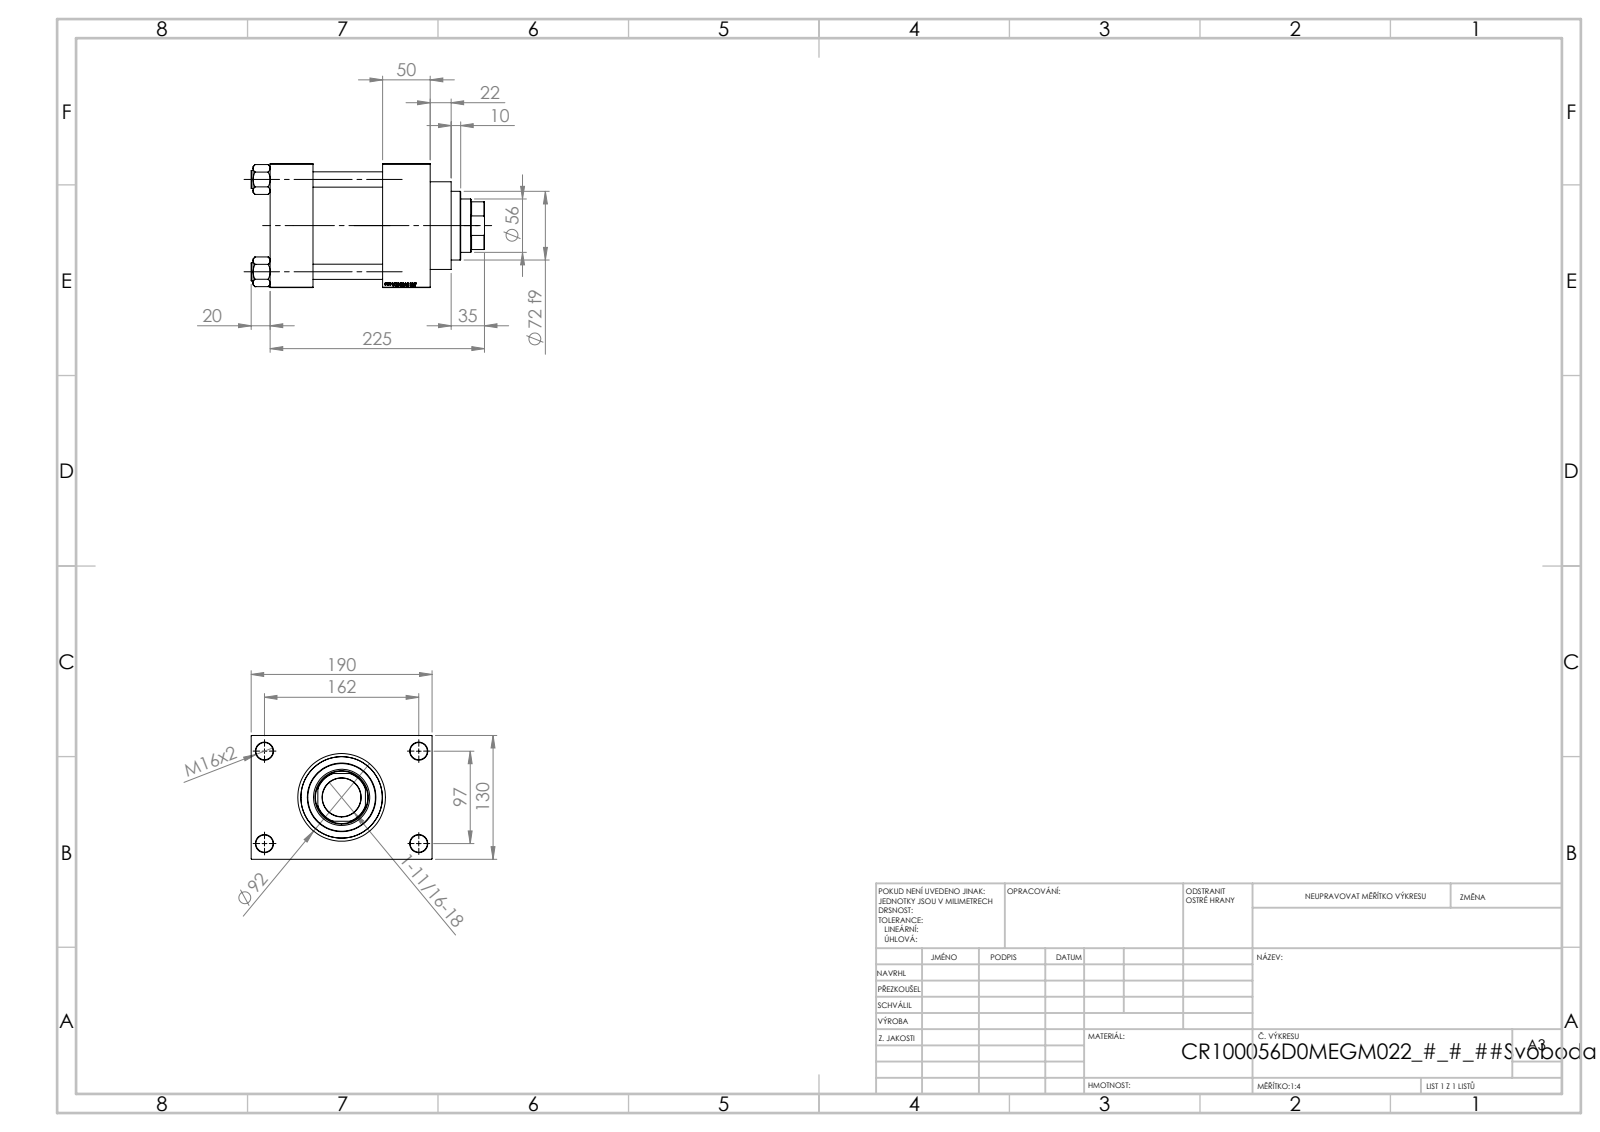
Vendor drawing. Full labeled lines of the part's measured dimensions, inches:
Part name (STEP PRODUCT): V215CR_D_TYCINKA; NUT_M5_D; V215_VC_A; V215CR_VCP_D (+1 more)
STEP written by: SolidWorks 2019 (CONFIG_CONTROL_DESIGN)
Units: inches
Bodies: 11 solids, 1152 faces (545 planar, 89 cylindrical, 518 other)
Overall size (bounding box): 9.646 × 7.48 × 5.118
Volume: 161.9 in³ · Surface area: 561 in²
Round holes (diameter × count): ⌀0.63 ×4, ⌀0.709 ×4, ⌀0.276 ×2, ⌀1.041 ×2, ⌀1.378 ×2, ⌀1.594 ×1, ⌀2.205 ×1, ⌀2.323 ×1, ⌀2.992 ×1, ⌀3.366 ×1, ⌀3.937 ×1
Round bosses / shafts (diameter × count): ⌀0.748 ×4, ⌀4.173 ×1, ⌀3.622 ×1, ⌀2.835 ×1
Partial cylindrical surfaces — rounded edges, fillets, slot ends (radius × count): R1.063 ×1
Main face-to-face distances: 5.118, 1.969, 1.772, 4.646, 2.874, 4.843, 6.614, 1.181, 6.299, 7.48
Hole centre spacings: 1.281, 2.698, 3.717, 3.815, 4.026, 5.096, 6.367, 3.819
